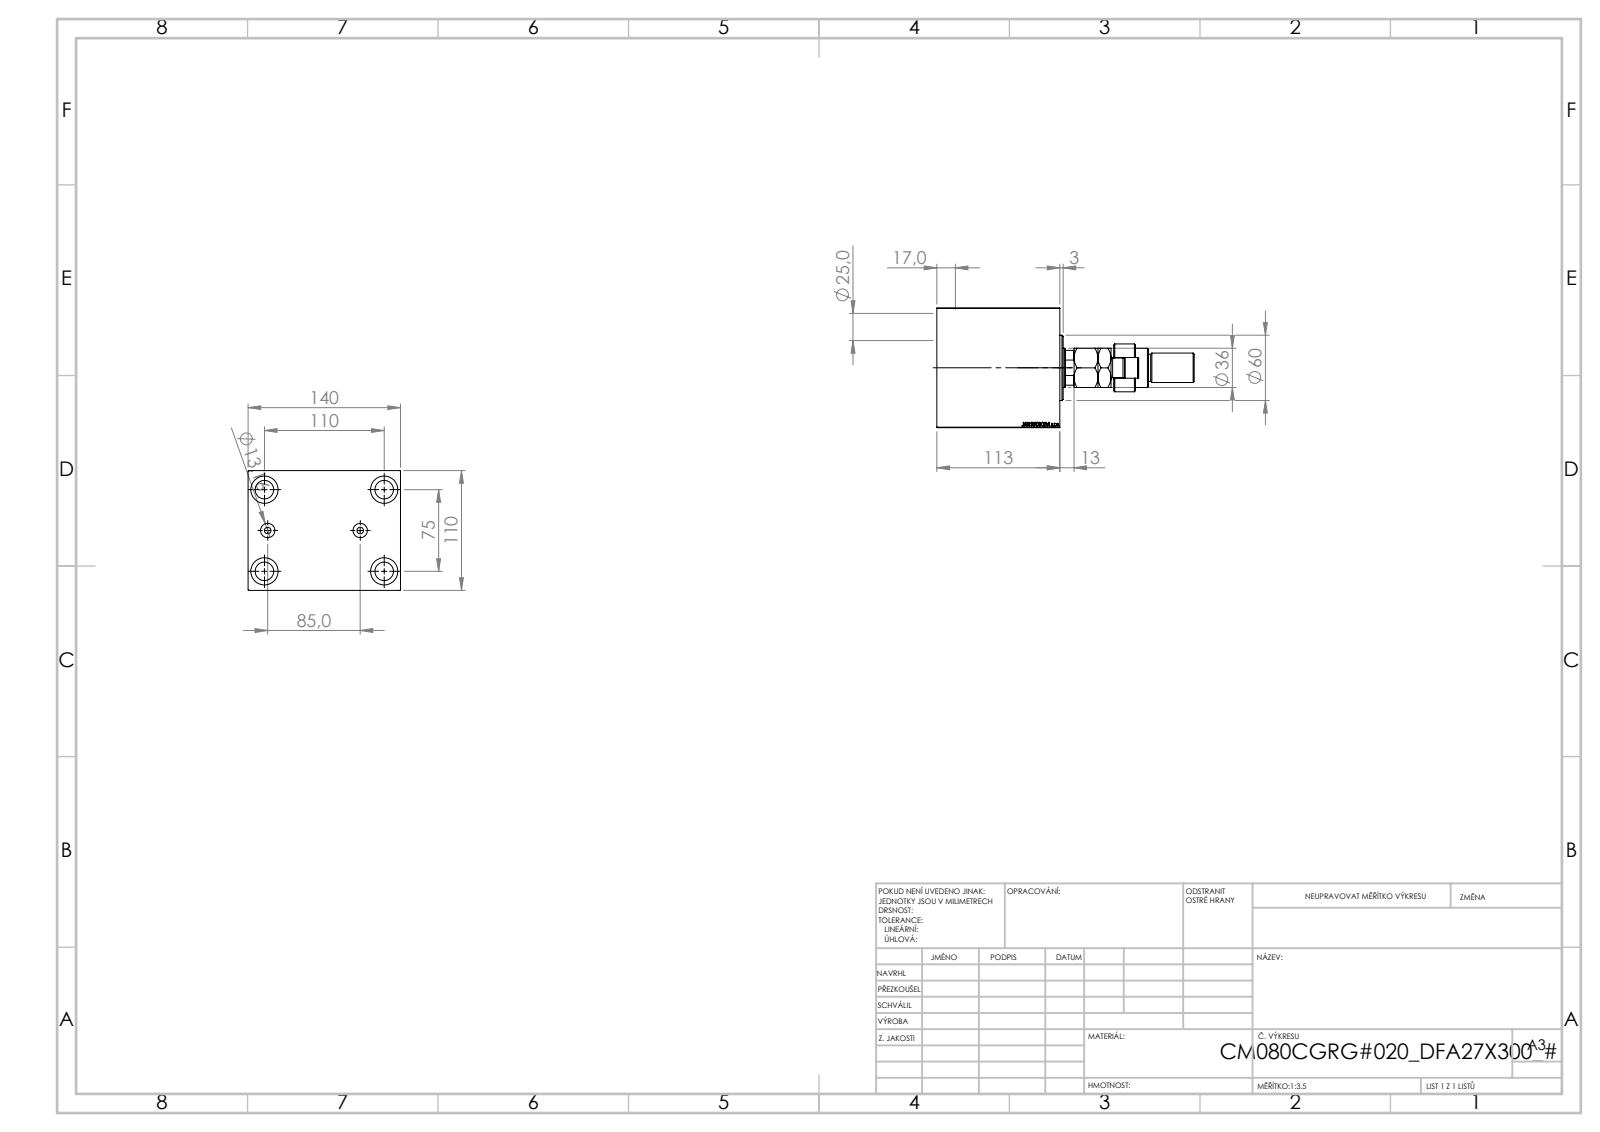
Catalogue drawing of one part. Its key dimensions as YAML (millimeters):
part_name: "V450CM_C_Body; FEMALE_PART_FOR_DFA; MFA; V450CM_VC_B (+1 more)"
step_written_by: "SolidWorks 2019 (CONFIG_CONTROL_DESIGN)"
units: millimeters
bodies: {solids: 5, faces: 948, planar: 439, cylindrical: 71, other: 438}
overall_size: [237.5, 140, 110]
volume: 1613000
surface_area: 190401
round_holes:
  - {diameter: 17, count: 4}
  - {diameter: 25, count: 4}
  - {diameter: 6, count: 2}
  - {diameter: 13.16, count: 2}
  - {diameter: 25.5, count: 1}
  - {diameter: 39.5, count: 1}
  - {diameter: 80, count: 1}
  - {diameter: 82, count: 1}
  - {diameter: 87, count: 1}
round_bosses_or_shafts:
  - {diameter: 60, count: 1}
  - {diameter: 44, count: 1}
  - {diameter: 36, count: 1}
  - {diameter: 28, count: 1}
  - {diameter: 27, count: 1}
  - {diameter: 25, count: 1}
  - {diameter: 18, count: 1}
partial_cylinders:
  - {radius: 9.5, count: 1}
  - {radius: 15, count: 1}
  - {radius: 17.5, count: 1}
face_to_face_distances: [110, 140, 113, 57.25, 55.75, 10, 20, 103, 83, 45.75]
hole_center_spacings: [39.53, 66.57, 104.46, 42.5, 75, 110, 133.14, 85]
